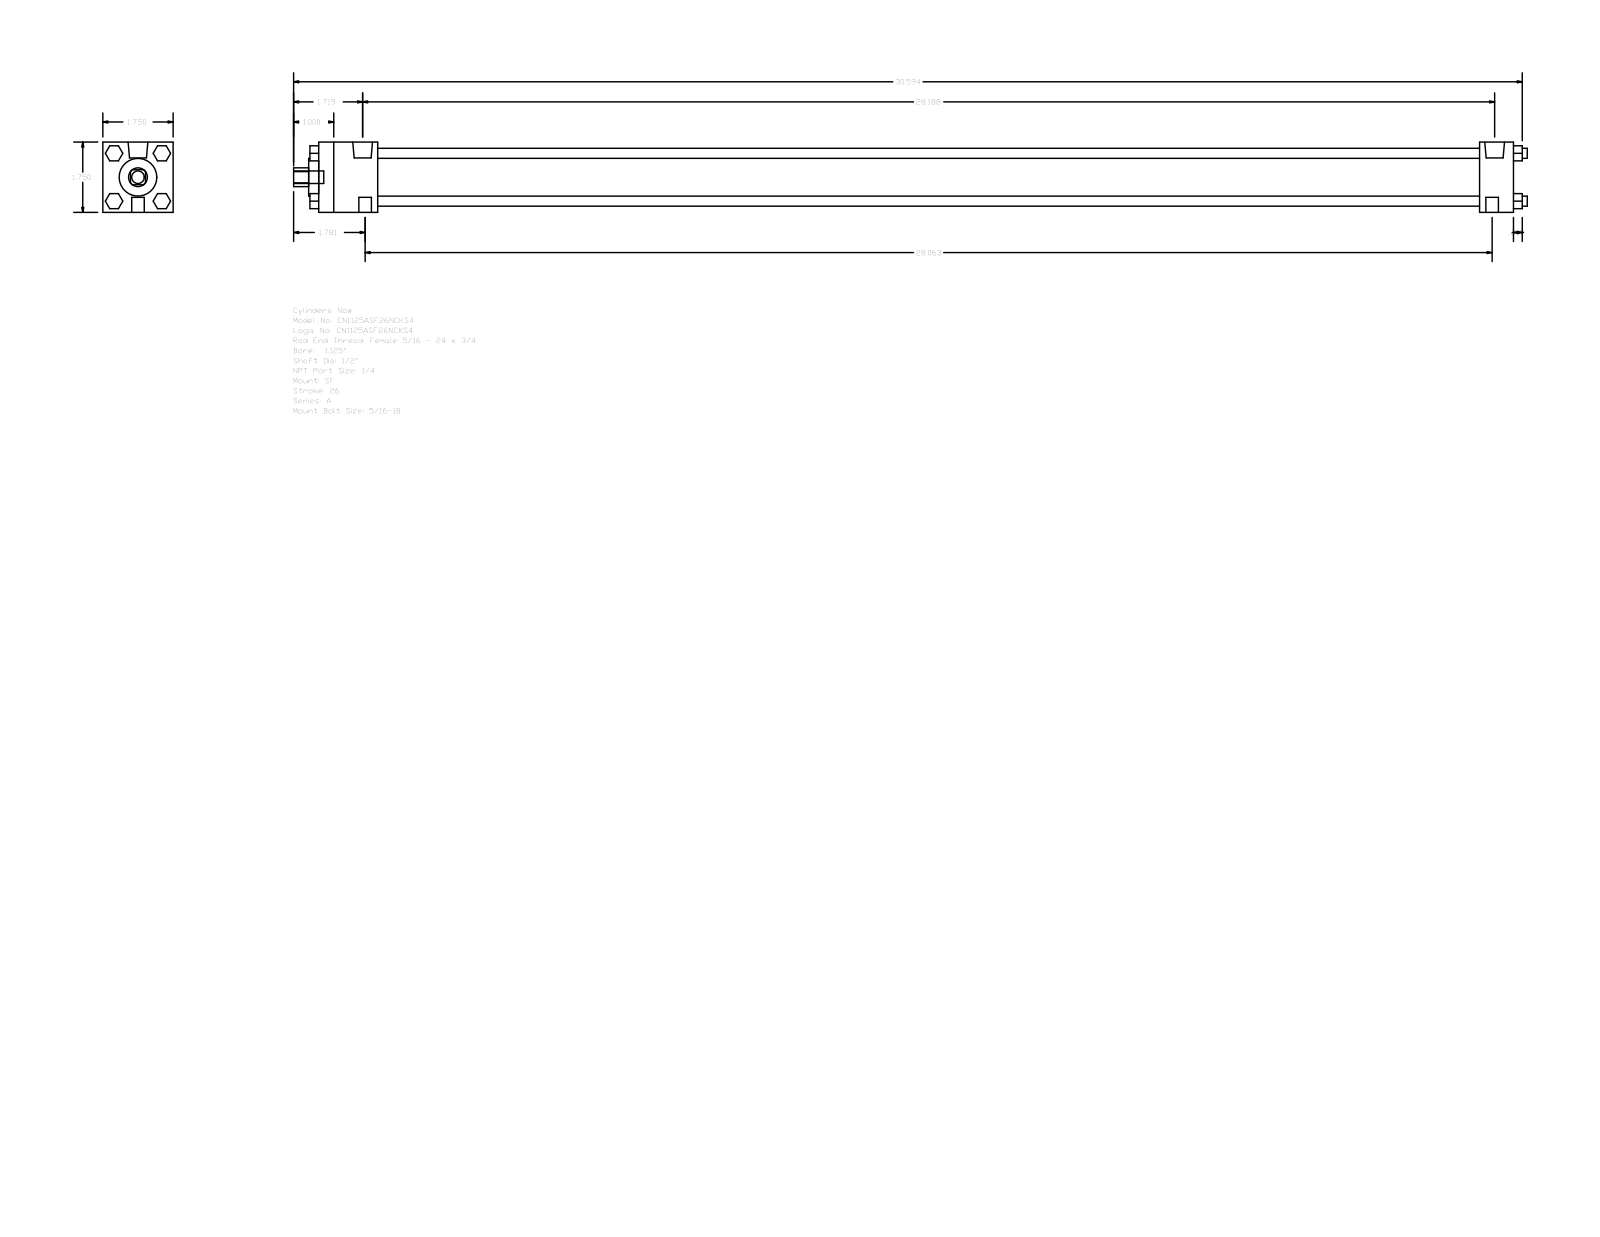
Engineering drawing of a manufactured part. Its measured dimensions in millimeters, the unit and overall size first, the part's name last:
Units: millimetres
Overall size (bounding box): 780.26 × 44.45 × 44.45
Round holes (diameter × count): ⌀12.7 ×1, ⌀23.81 ×1, ⌀31.88 ×1
Round bosses / shafts (diameter × count): ⌀6.35 ×4, ⌀7.94 ×3, ⌀12.49 ×2, ⌀5.56 ×2
Partial cylindrical surfaces — rounded edges, fillets, slot ends (radius × count): R5.94 ×1
Main face-to-face distances: 44.46, 755.64, 734.21, 21.43, 37.3, 696.91, 718.34, 9.53, 5.59, 9.52
Bodies: 0 solids, 120 faces (92 planar, 28 cylindrical, 0 other)
Part name (STEP PRODUCT): A_SF__0112_0.5
STEP written by: GSSL Pune (CONFIG_CONTROL_DESIGN)
